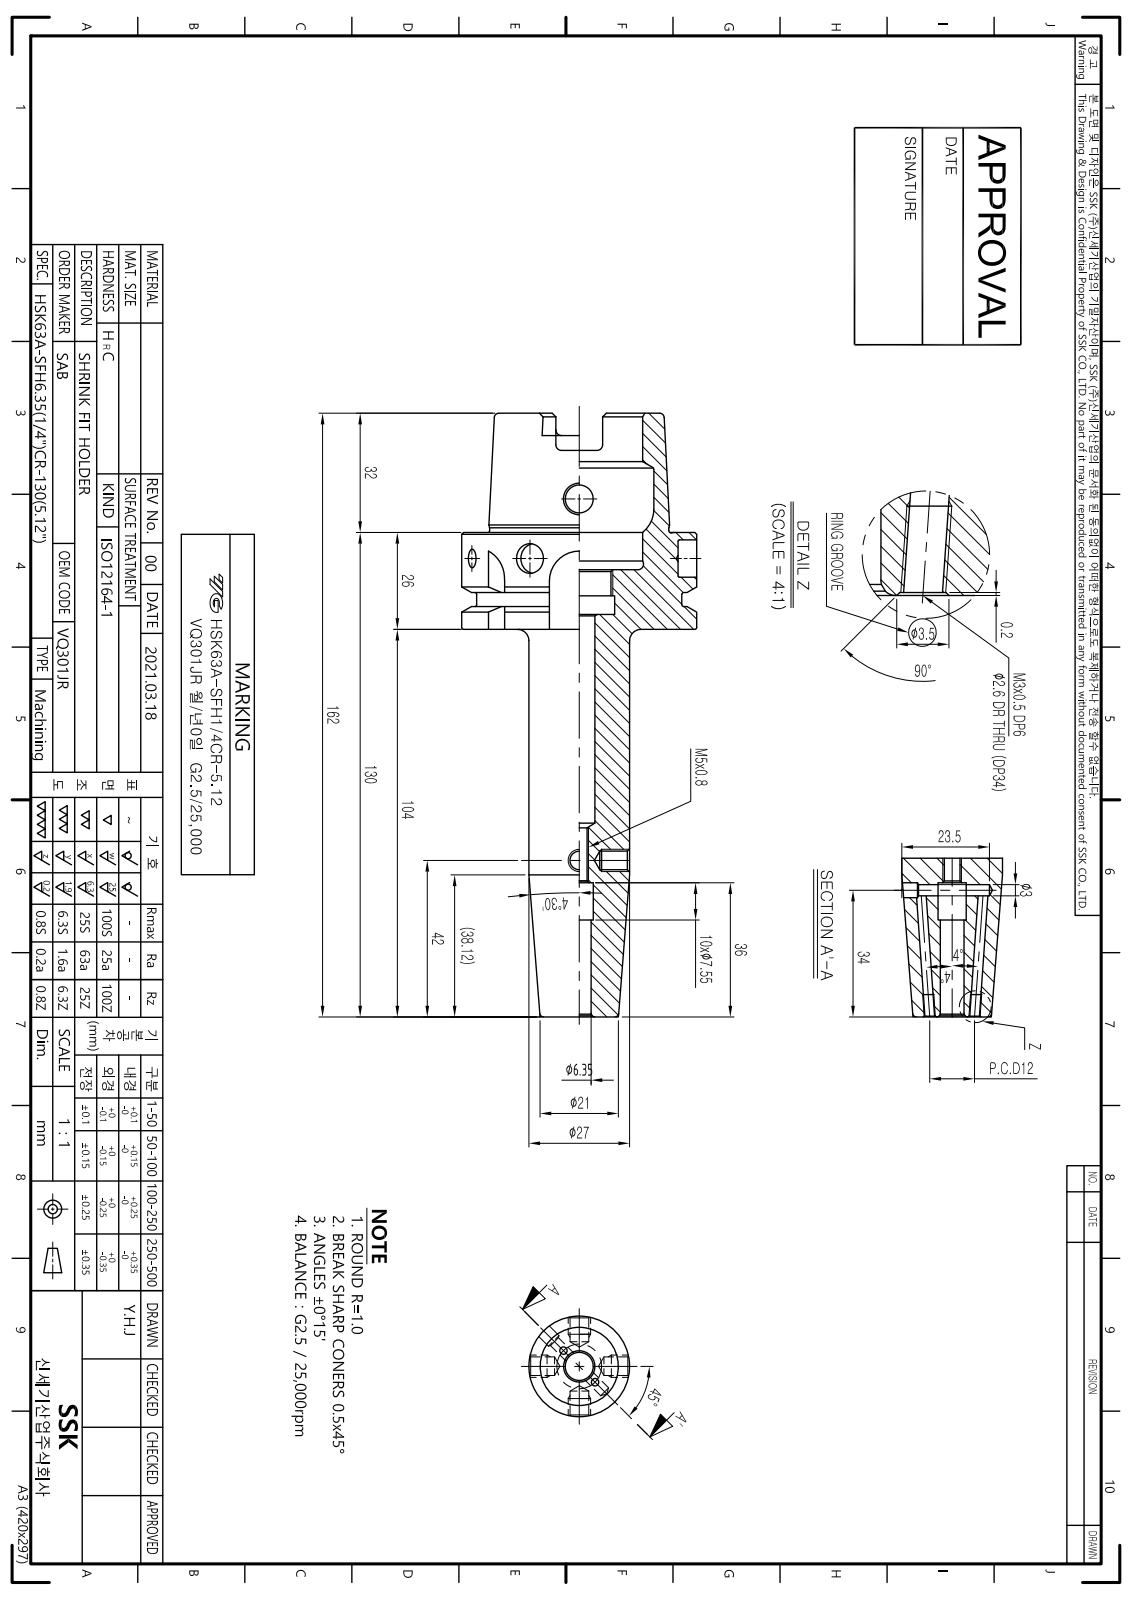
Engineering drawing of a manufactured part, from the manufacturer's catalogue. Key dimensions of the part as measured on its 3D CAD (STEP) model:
Part name (STEP PRODUCT): LO-HSK63A-SFH6.35CR-130
STEP written by: Autodesk Inventor 2022 (AUTOMOTIVE_DESIGN)
Units: millimetres
Bodies: 1 solid, 121 faces (42 planar, 36 cylindrical, 43 other)
Overall size (bounding box): 162 × 63 × 63
Volume: 131 923 mm³ · Surface area: 33 354 mm²
Round holes (diameter × count): ⌀2.46 ×2, ⌀4.3 ×1, ⌀6.35 ×1, ⌀7.5 ×1, ⌀7.55 ×1, ⌀8.4 ×1, ⌀10 ×1, ⌀16.92 ×1, ⌀19 ×1, ⌀34 ×1, ⌀40 ×1
Round bosses / shafts (diameter × count): ⌀63 ×1, ⌀55 ×1, ⌀48.04 ×1, ⌀27 ×1
Partial cylindrical surfaces — rounded edges, fillets, slot ends (radius × count): R1.5 ×6, R2.88 ×4, R8 ×4
Main face-to-face distances: 26, 10, 16, 32, 42, 58, 53, 22, 4, 12
